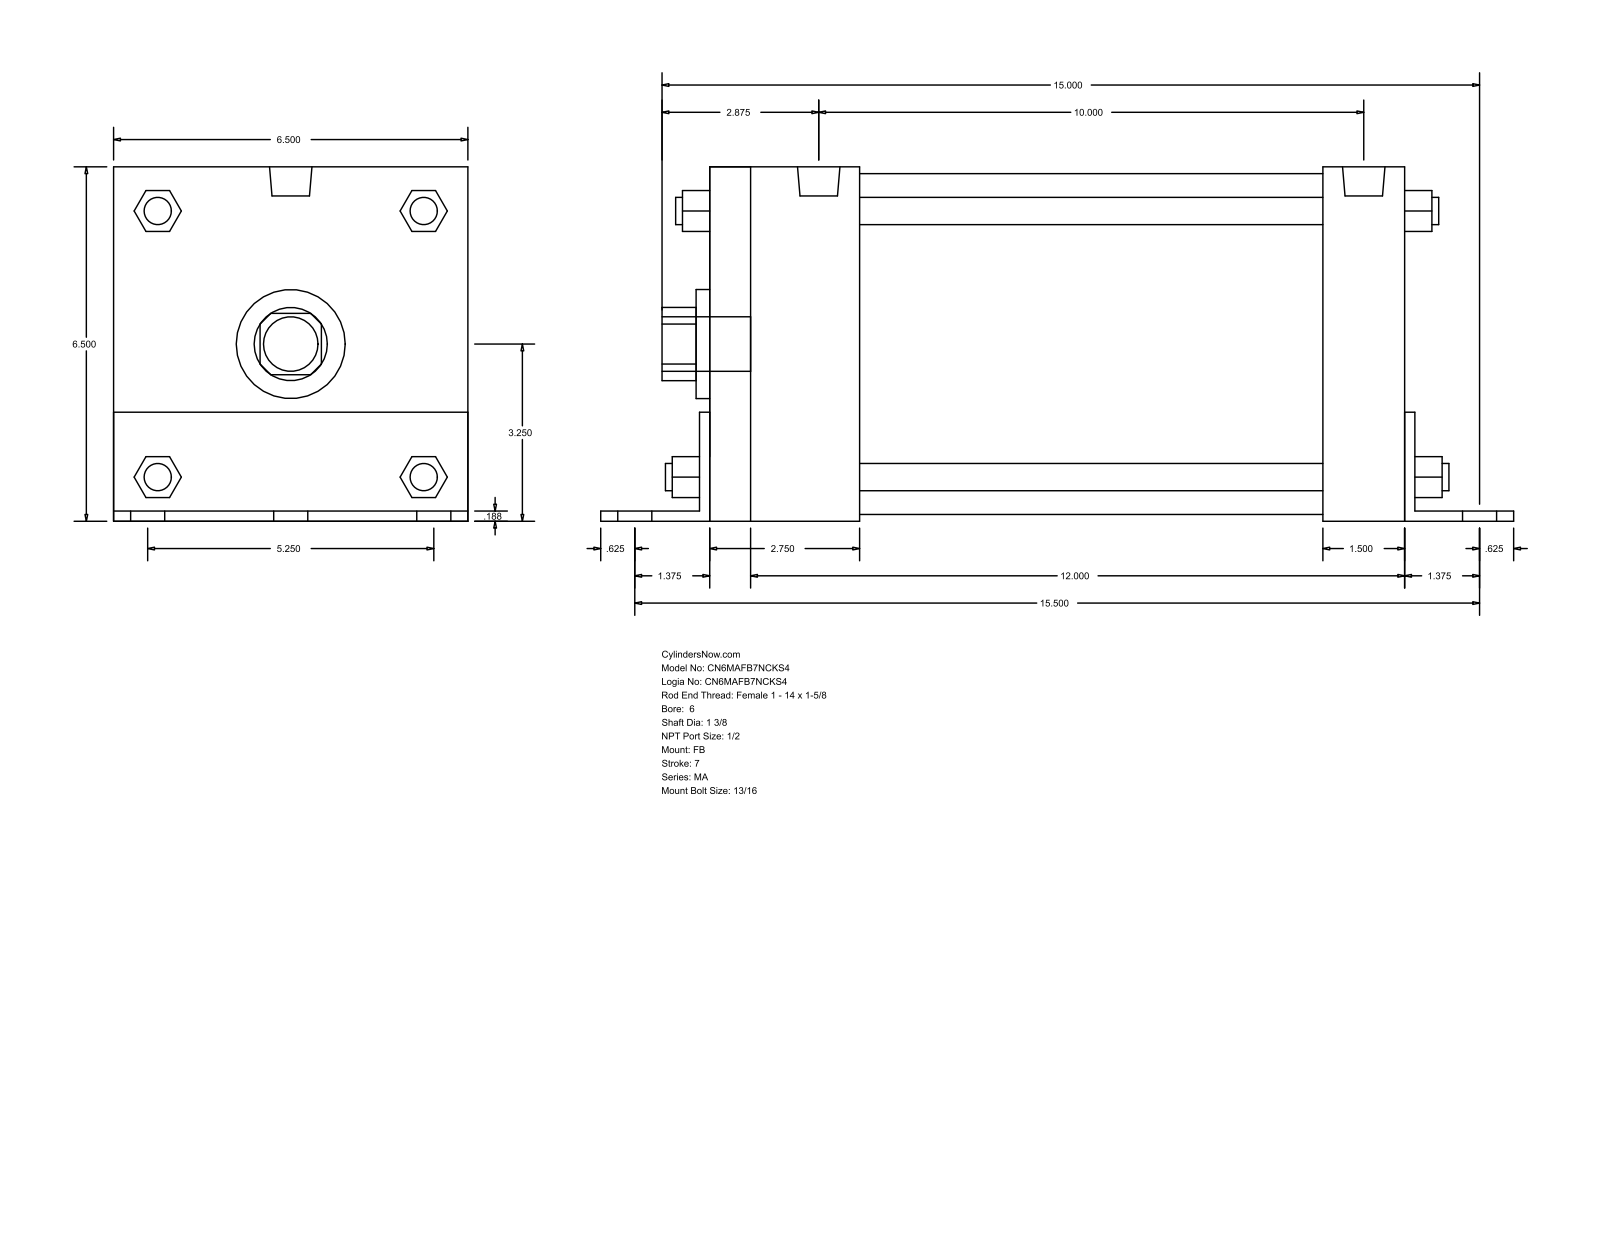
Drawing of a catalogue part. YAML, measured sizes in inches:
part_name: "MA_FB__0600_1.375"
step_written_by: "GSSL Pune (CONFIG_CONTROL_DESIGN)"
units: inches
bodies: {solids: 0, faces: 140, planar: 105, cylindrical: 35, other: 0}
overall_size: [16.625, 6.502, 6.5]
round_holes:
  - {diameter: 1.375, count: 1}
  - {diameter: 2, count: 1}
  - {diameter: 6.25, count: 1}
round_bosses_or_shafts:
  - {diameter: 0.813, count: 6}
  - {diameter: 0.687, count: 4}
  - {diameter: 0.5, count: 4}
  - {diameter: 0.778, count: 2}
  - {diameter: 1, count: 1}
partial_cylinders:
  - {radius: 0.672, count: 1}
  - {radius: 1.262, count: 1}
face_to_face_distances: [6.5, 0.187, 12.625, 6.502, 0.185, 6.315, 0.188, 1.5, 12.813, 13]
